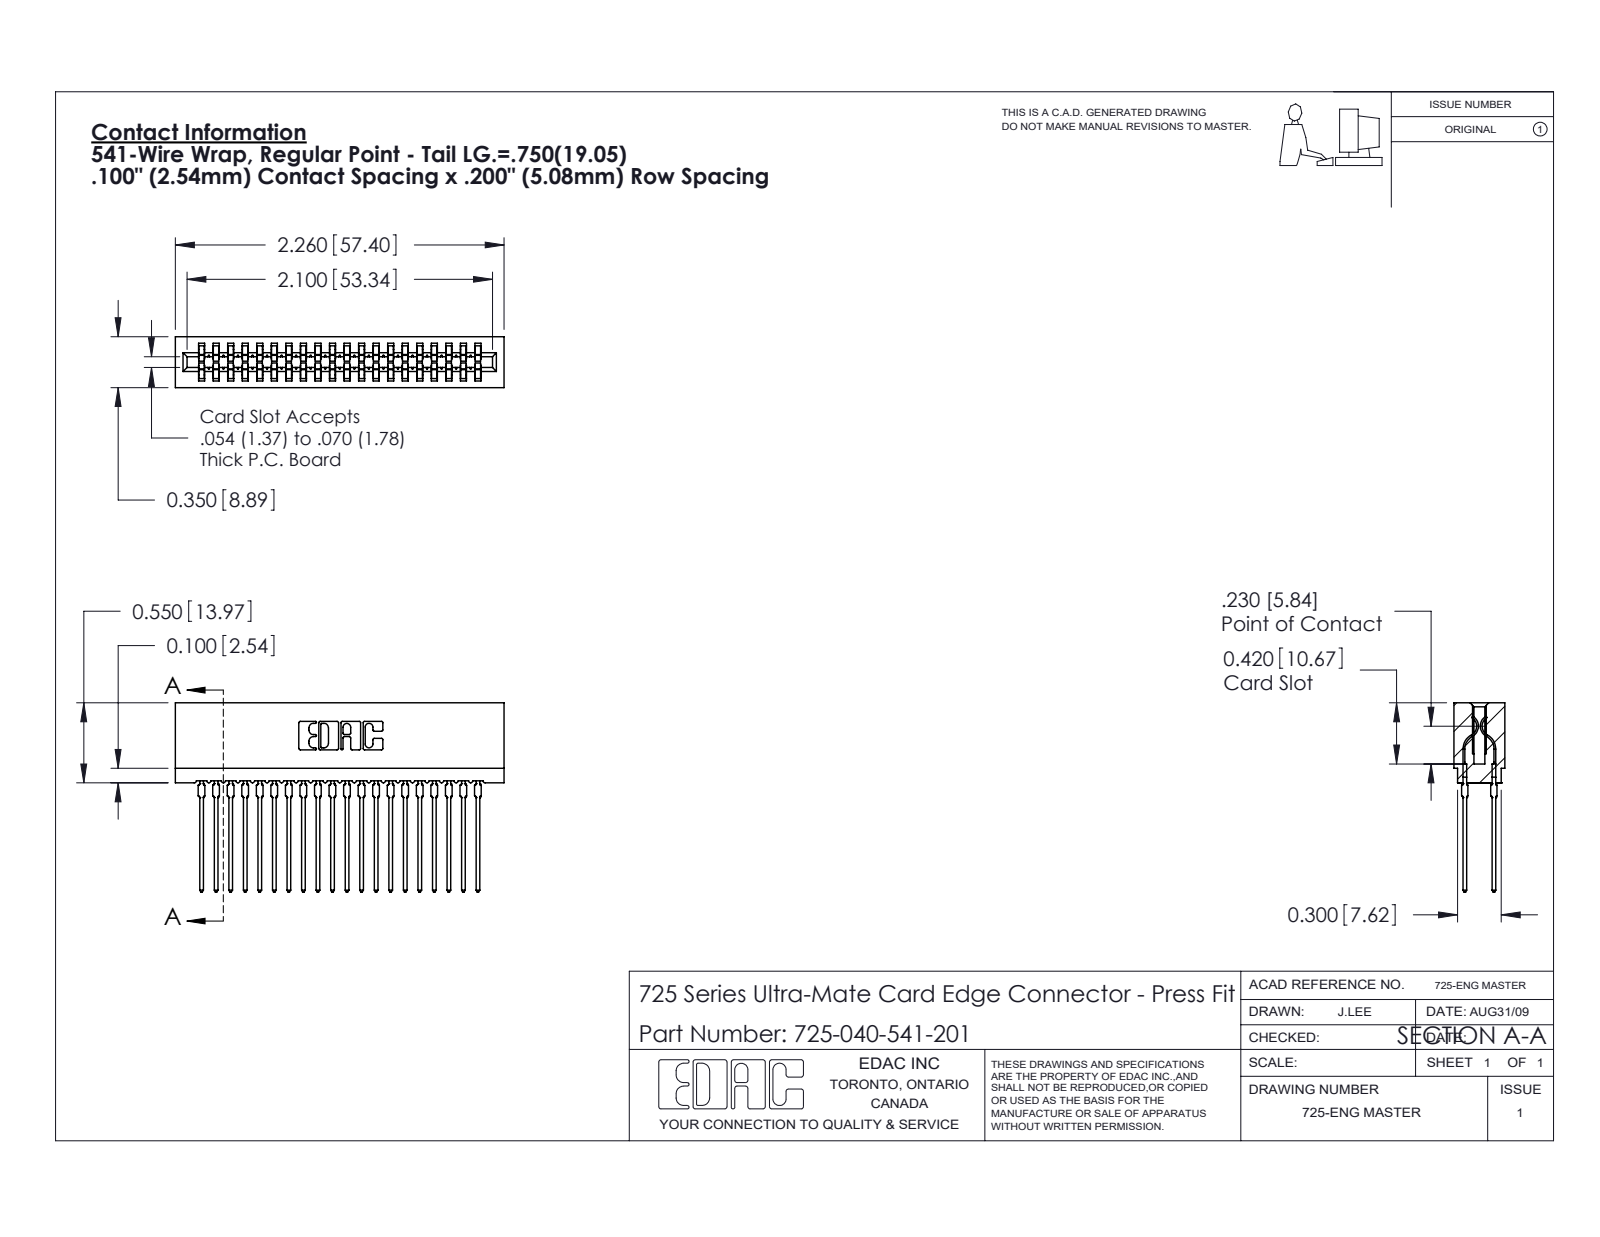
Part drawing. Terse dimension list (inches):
name: 745-292-001_541; 725-040-541-201; 725 Part_Insulator Option - 01
written by: SolidWorks 2020 (CONFIG_CONTROL_DESIGN)
unit: in
bodies: 41 solids, 3675 faces (1895 planar, 740 cylindrical, 1040 other)
size: 2.26 × 1.301 × 0.35
volume: 0.297 in³; area: 16.4 in²
rounds: 80× R0.021, 40× R0.015, 22× R0.01, 8× R0.005, 8× R0.011, 6× R0.007, 6× R0.031, 3× R0.026
face distances: 0.2, 0.1, 0.063, 0.287, 0.4, 0.3, 0.5, 0.6, 0.7, 0.35
